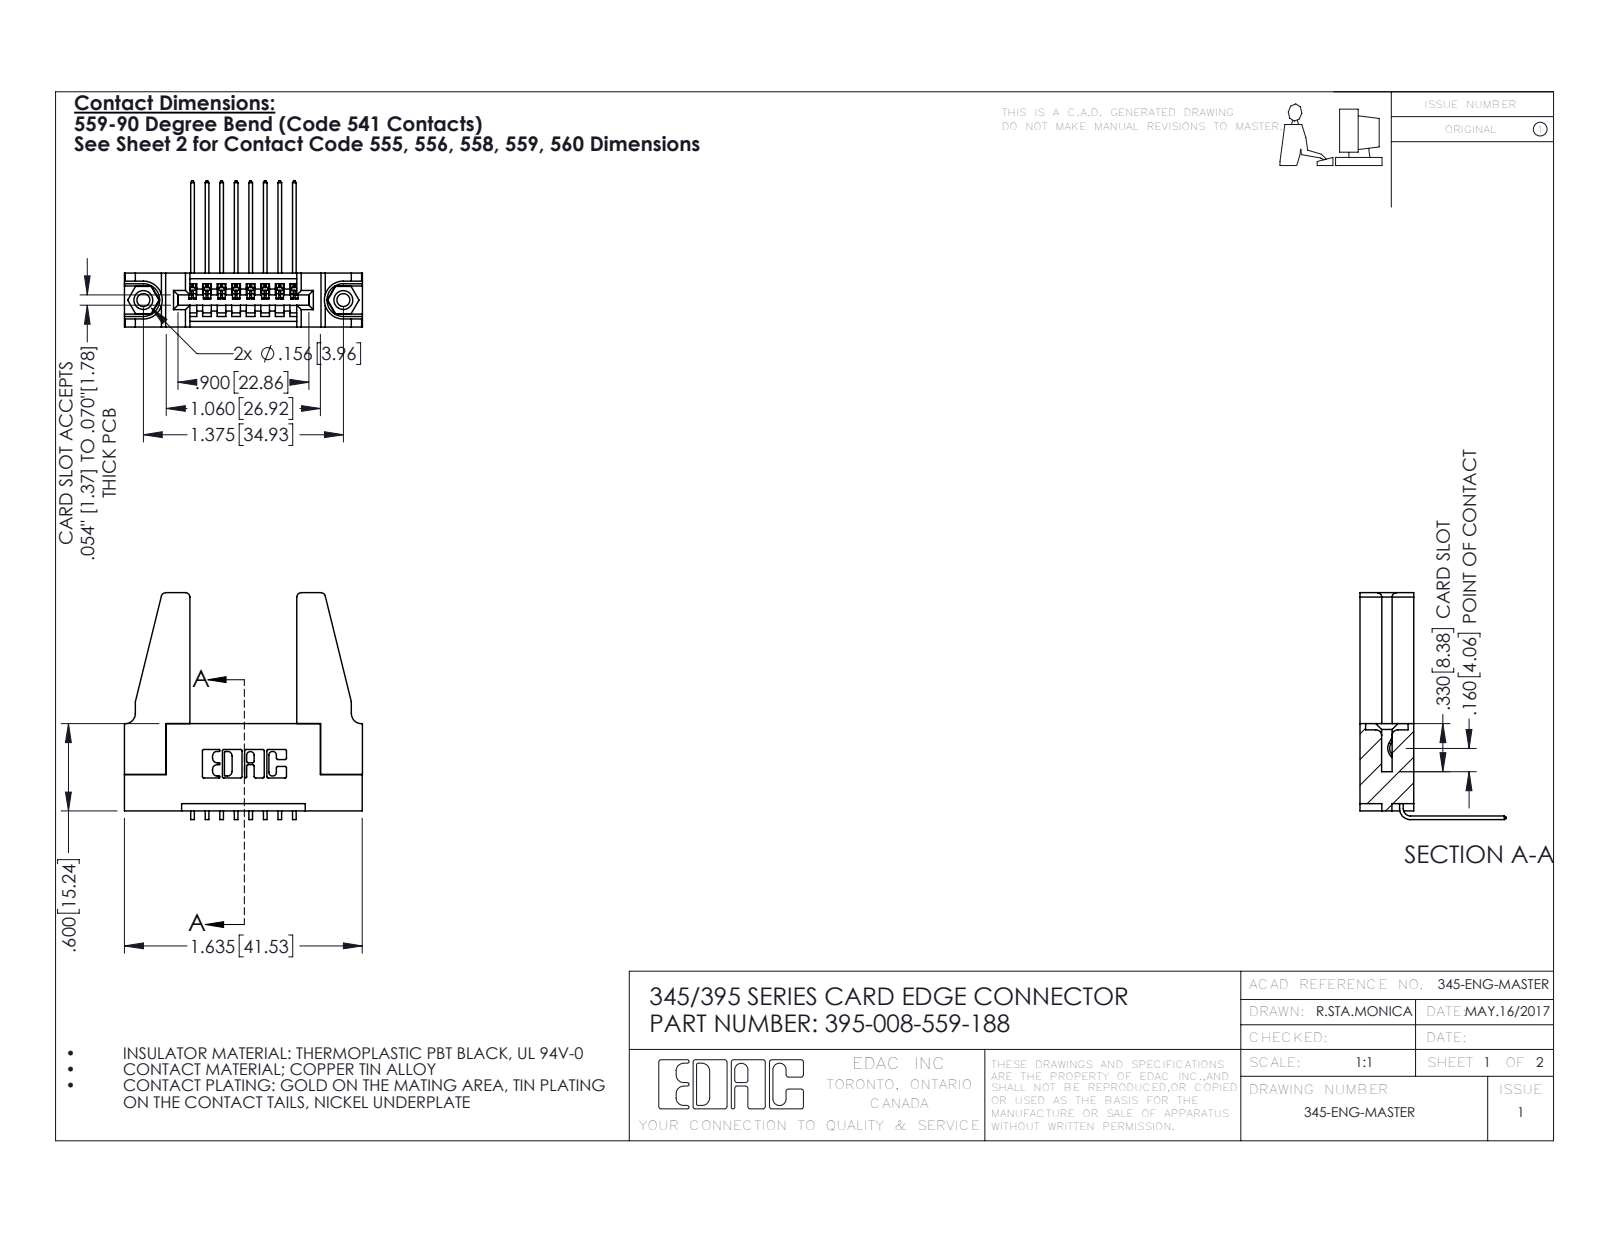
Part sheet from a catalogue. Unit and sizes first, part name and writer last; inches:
Units: inches
Overall size (bounding box): 1.636 × 1.559 × 1.005
Round holes (diameter × count): ⌀0.089 ×2, ⌀0.125 ×2, ⌀0.156 ×2, ⌀0.064 ×1
Round bosses / shafts (diameter × count): ⌀0.155 ×2
Partial cylindrical surfaces — rounded edges, fillets, slot ends (radius × count): R0.01 ×22, R0.006 ×16, R0.03 ×8, R0.007 ×6, R0.031 ×6, R0.026 ×3, R0.031 ×2, R0.04 ×2
Main face-to-face distances: 0.37, 0.072, 0.2, 0.298, 0.15, 0.148, 0.35, 0.098, 0.272, 0.025
Hole centre spacings: 0.27, 1.144, 1.375
Volume: 0.424 in³ · Surface area: 11.99 in²
Bodies: 13 solids, 730 faces (488 planar, 226 cylindrical, 16 other)
Part name (STEP PRODUCT): 345-220-078_345-220-088; 345 Part_Flush Mounting Lugs - 0.156 Dia-TH; 395-008-559-188; 345-250-001_345-250-001-102 (+1 more)
STEP written by: SolidWorks 2016 (CONFIG_CONTROL_DESIGN)
